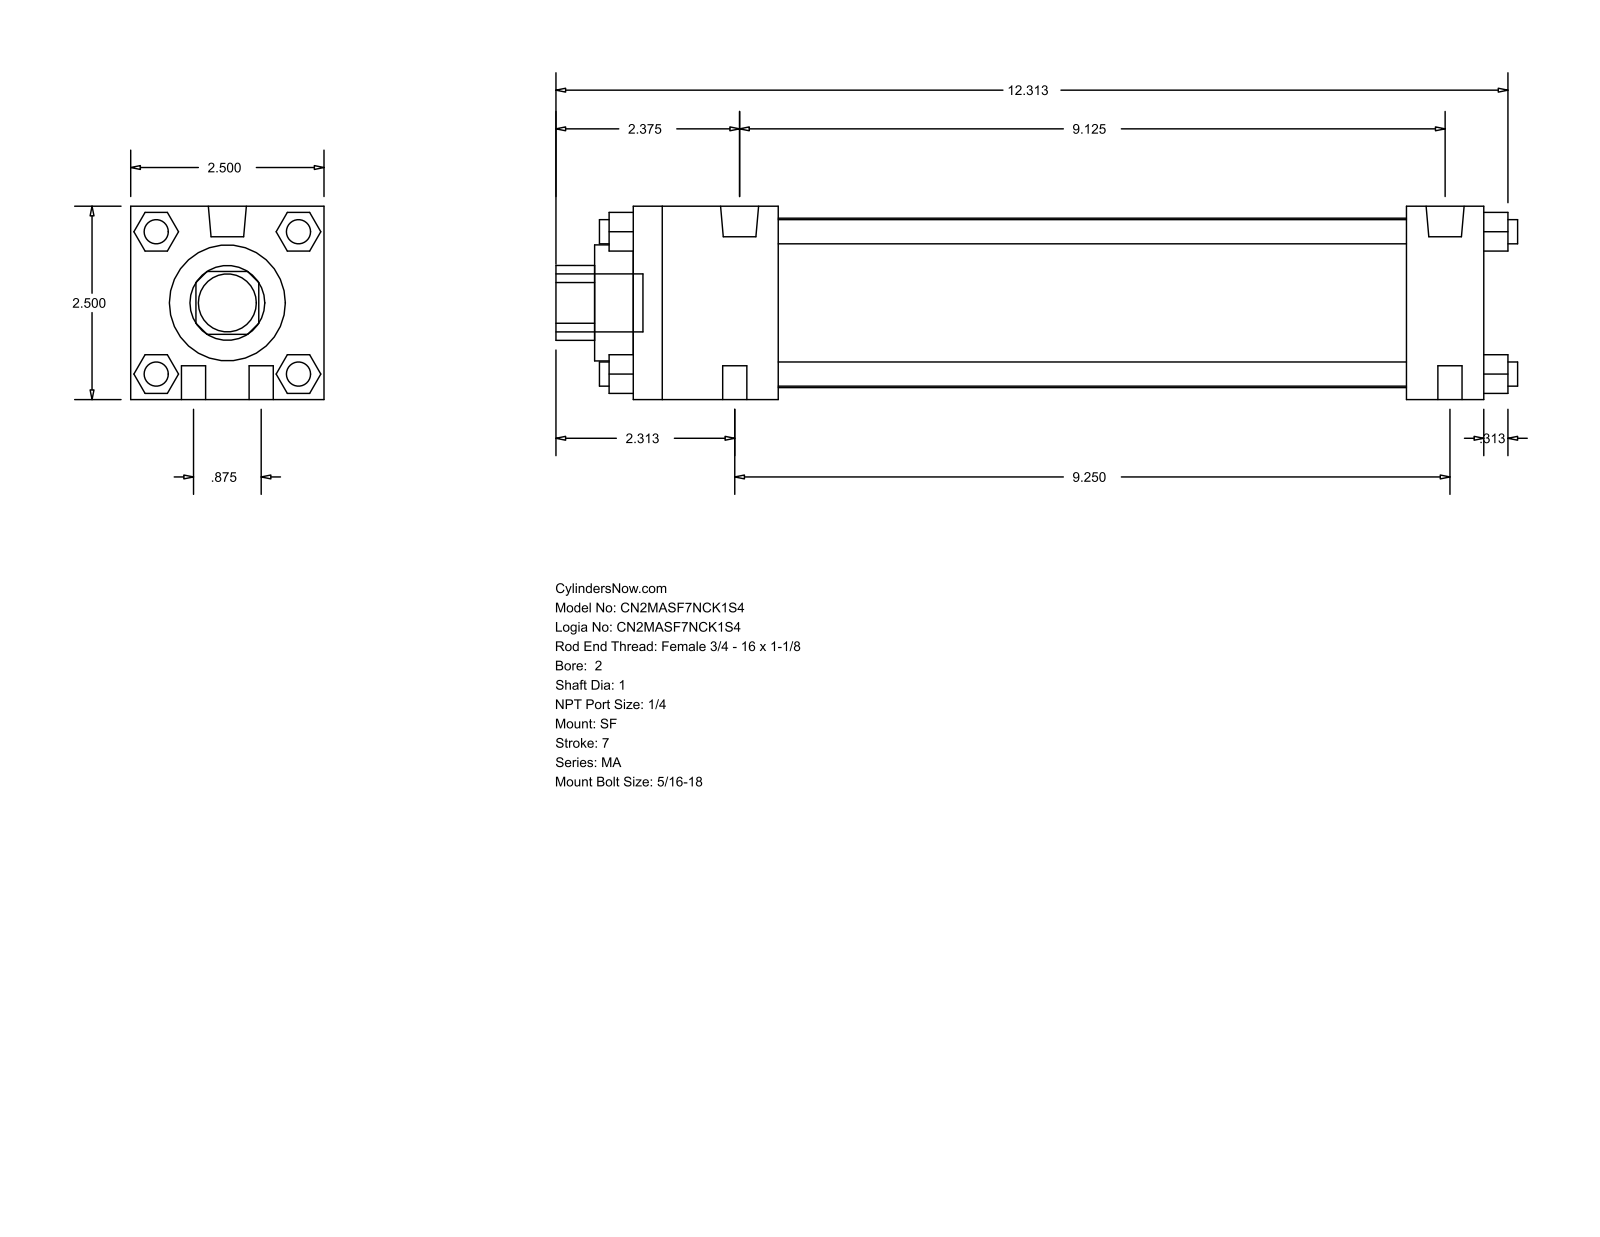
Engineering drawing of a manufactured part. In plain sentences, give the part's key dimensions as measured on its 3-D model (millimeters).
The part is named "MA_SF__0200_1". Its 3-D file was written by "GSSL Pune (CONFIG_CONTROL_DESIGN)". It is 0 solids with 124 faces: 94 planar, 30 cylindrical and 0 other. Overall it measures 315.91 by 63.5 by 63.5 millimeters. Round holes: 1 of diameter 25.4, 1 of diameter 38.1, 1 of diameter 55.63. Round bosses or shafts: 10 of diameter 7.94, 2 of diameter 12.49, 1 of diameter 19.05. Partial cylindrical surfaces (rounded edges, fillets, slot ends): 1 of radius 12.29. The main face-to-face distances are 63.5, 279.4, 12.7, 25.4, 254, 47.63, 206.37, 231.77, 23.37, 40.47.
